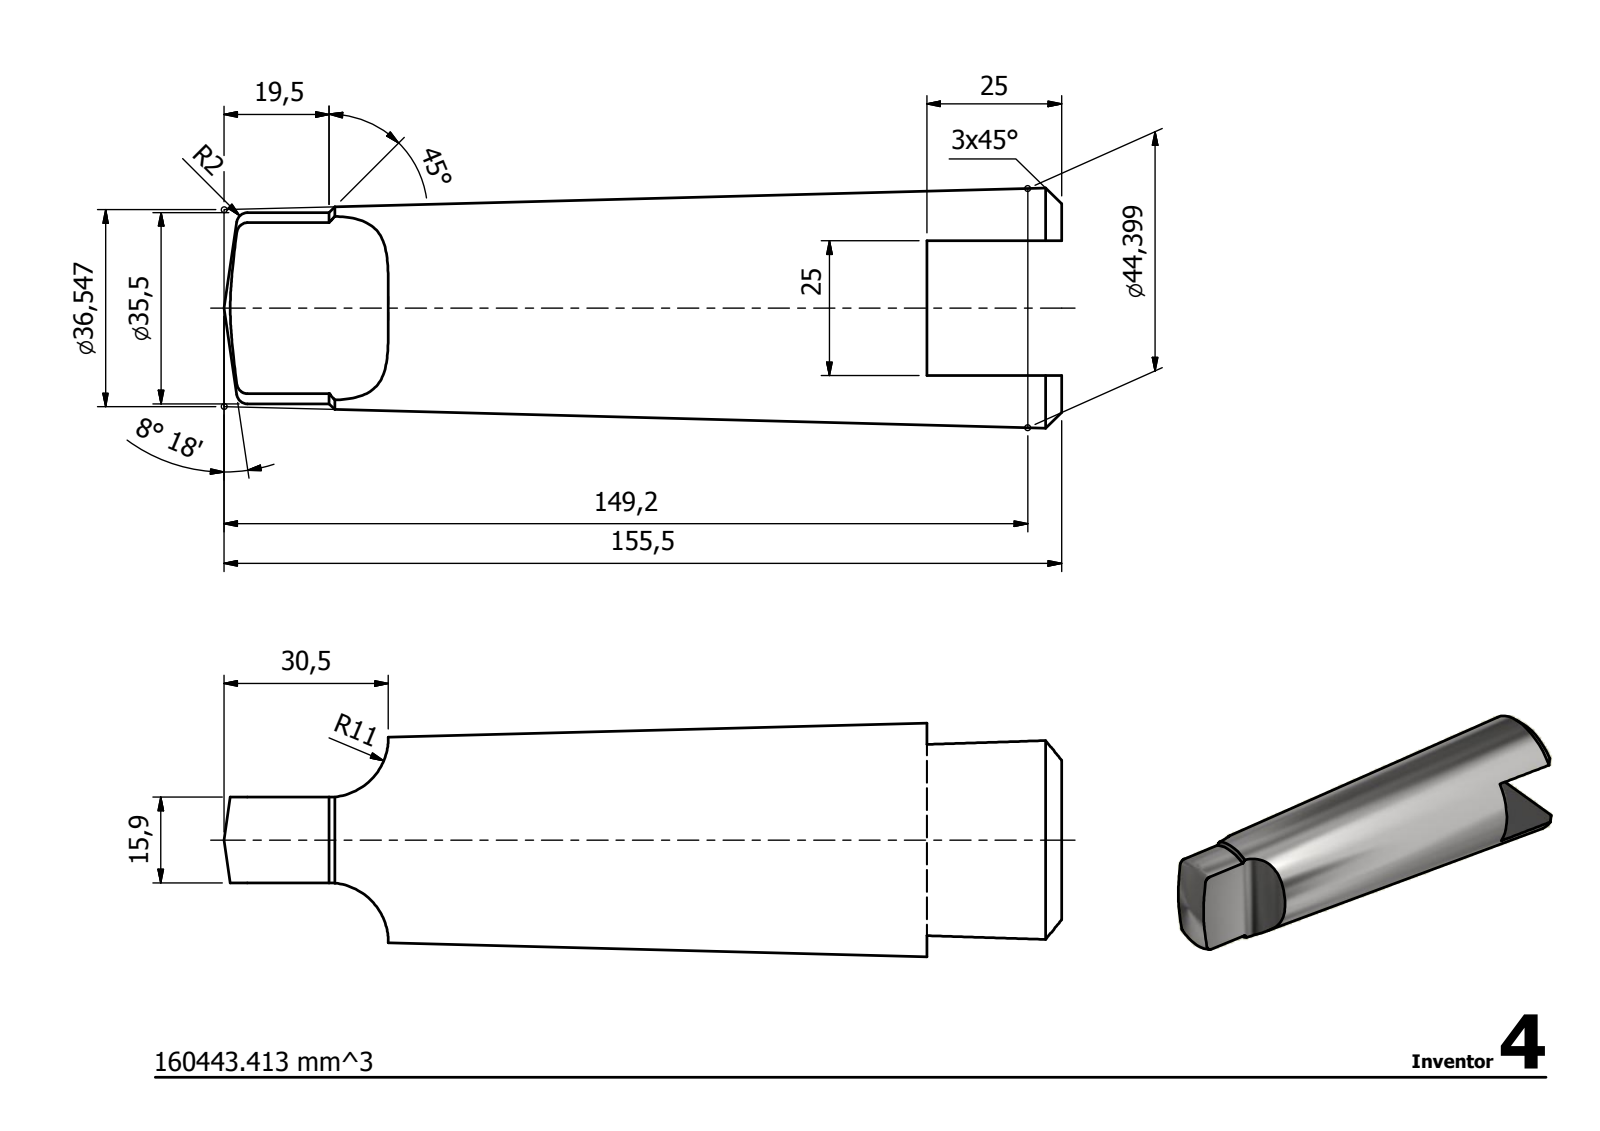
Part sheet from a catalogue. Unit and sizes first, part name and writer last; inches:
Units: inches
Overall size (bounding box): 6.122 × 1.755 × 1.709
Partial cylindrical surfaces — rounded edges, fillets, slot ends (radius × count): R0.433 ×2, R0.699 ×1
Main face-to-face distances: 0.984, 0.626
Volume: 9.792 in³ · Surface area: 33.77 in²
Bodies: 1 solid, 19 faces (7 planar, 4 cylindrical, 8 other)
STEP written by: Autodesk Inventor 2014 (AUTOMOTIVE_DESIGN)
